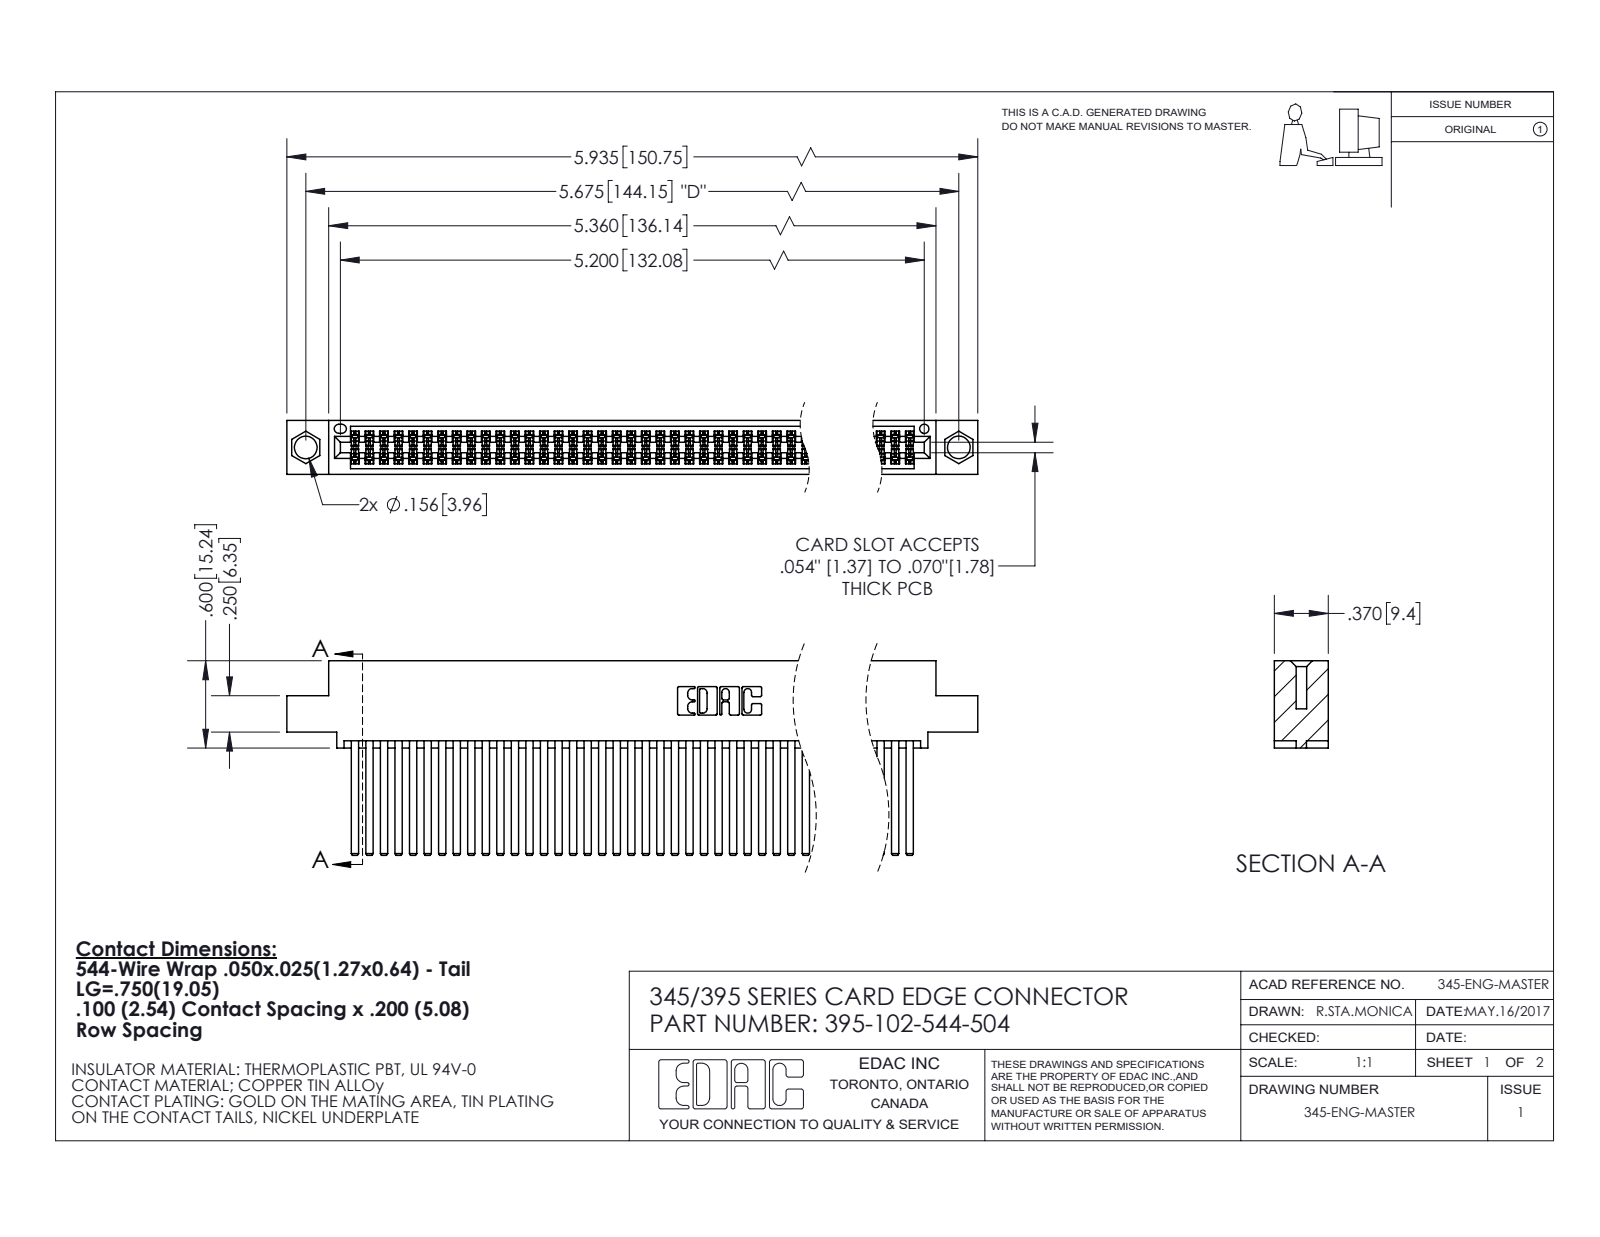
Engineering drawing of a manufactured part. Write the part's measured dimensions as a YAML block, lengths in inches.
part_name: "345 Part_0.110 Offset - 0.156 Dia-TI; 395-102-544-504; 345-292-001_345-293-144"
step_written_by: "SolidWorks 2020 (CONFIG_CONTROL_DESIGN)"
units: inches
bodies: {solids: 103, faces: 4632, planar: 3056, cylindrical: 1576, other: 0}
overall_size: [5.935, 1.337, 0.37]
volume: 0.975
surface_area: 43.29
round_holes:
  - {diameter: 0.156, count: 2}
  - {diameter: 0.064, count: 1}
partial_cylinders:
  - {radius: 0.006, count: 153}
  - {radius: 0.01, count: 22}
  - {radius: 0.007, count: 6}
  - {radius: 0.031, count: 6}
  - {radius: 0.026, count: 3}
  - {radius: 0.014, count: 2}
  - {radius: 0.019, count: 2}
  - {radius: 0.022, count: 2}
face_to_face_distances: [0.2, 0.025, 0.298, 0.072, 0.098, 0.272, 0.225, 0.175, 0.37, 0.05]
hole_center_spacings: [0.27, 5.439, 5.675]
